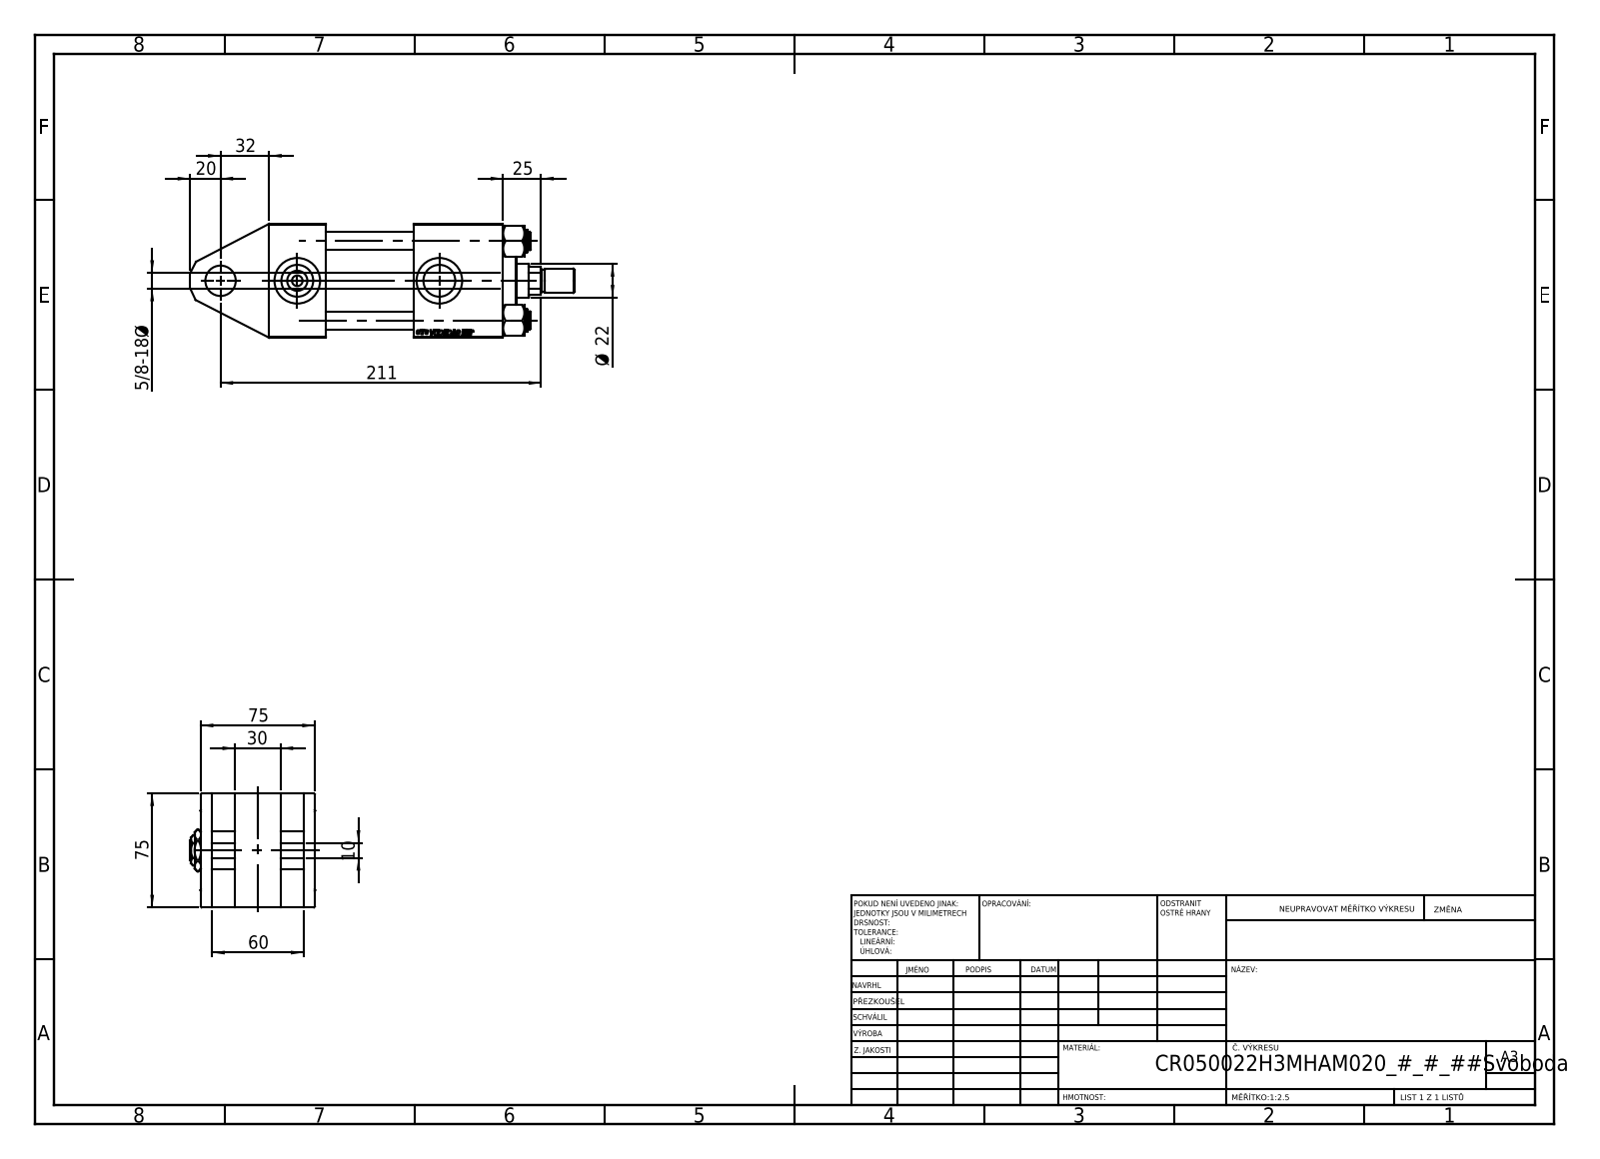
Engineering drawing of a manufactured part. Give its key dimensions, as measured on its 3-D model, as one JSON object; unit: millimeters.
{"part_name": "ROD_END_AH; V215CR_TYCINKA_H; V215CR_H_Body; Zatka_pro_OIL_PORT (+3 more)", "step_written_by": "SolidWorks 2019 (CONFIG_CONTROL_DESIGN)", "units": "millimeters", "bodies": {"solids": 14, "faces": 1243, "planar": 569, "cylindrical": 98, "other": 576}, "overall_size": [253, 82.27, 75], "volume_mm3": 732867, "surface_area_mm2": 168993, "round_holes": [[12, 4], [7, 2], [20.96, 2], [30, 2], [10.5, 1], [20, 1], [22, 1], [25, 1], [41, 1], [50, 1], [53, 1]], "round_bosses_or_shafts": [[15, 4], [56, 1], [34, 1], [16, 1], [14, 1]], "partial_cylinders_radius": [[10.5, 1]], "face_to_face_distances": [75, 117, 7.5, 67.5, 45, 22.5, 52.5, 15, 95, 59], "hole_center_spacings": [36.98, 52.3, 73.96, 50.5, 93.5, 144]}
